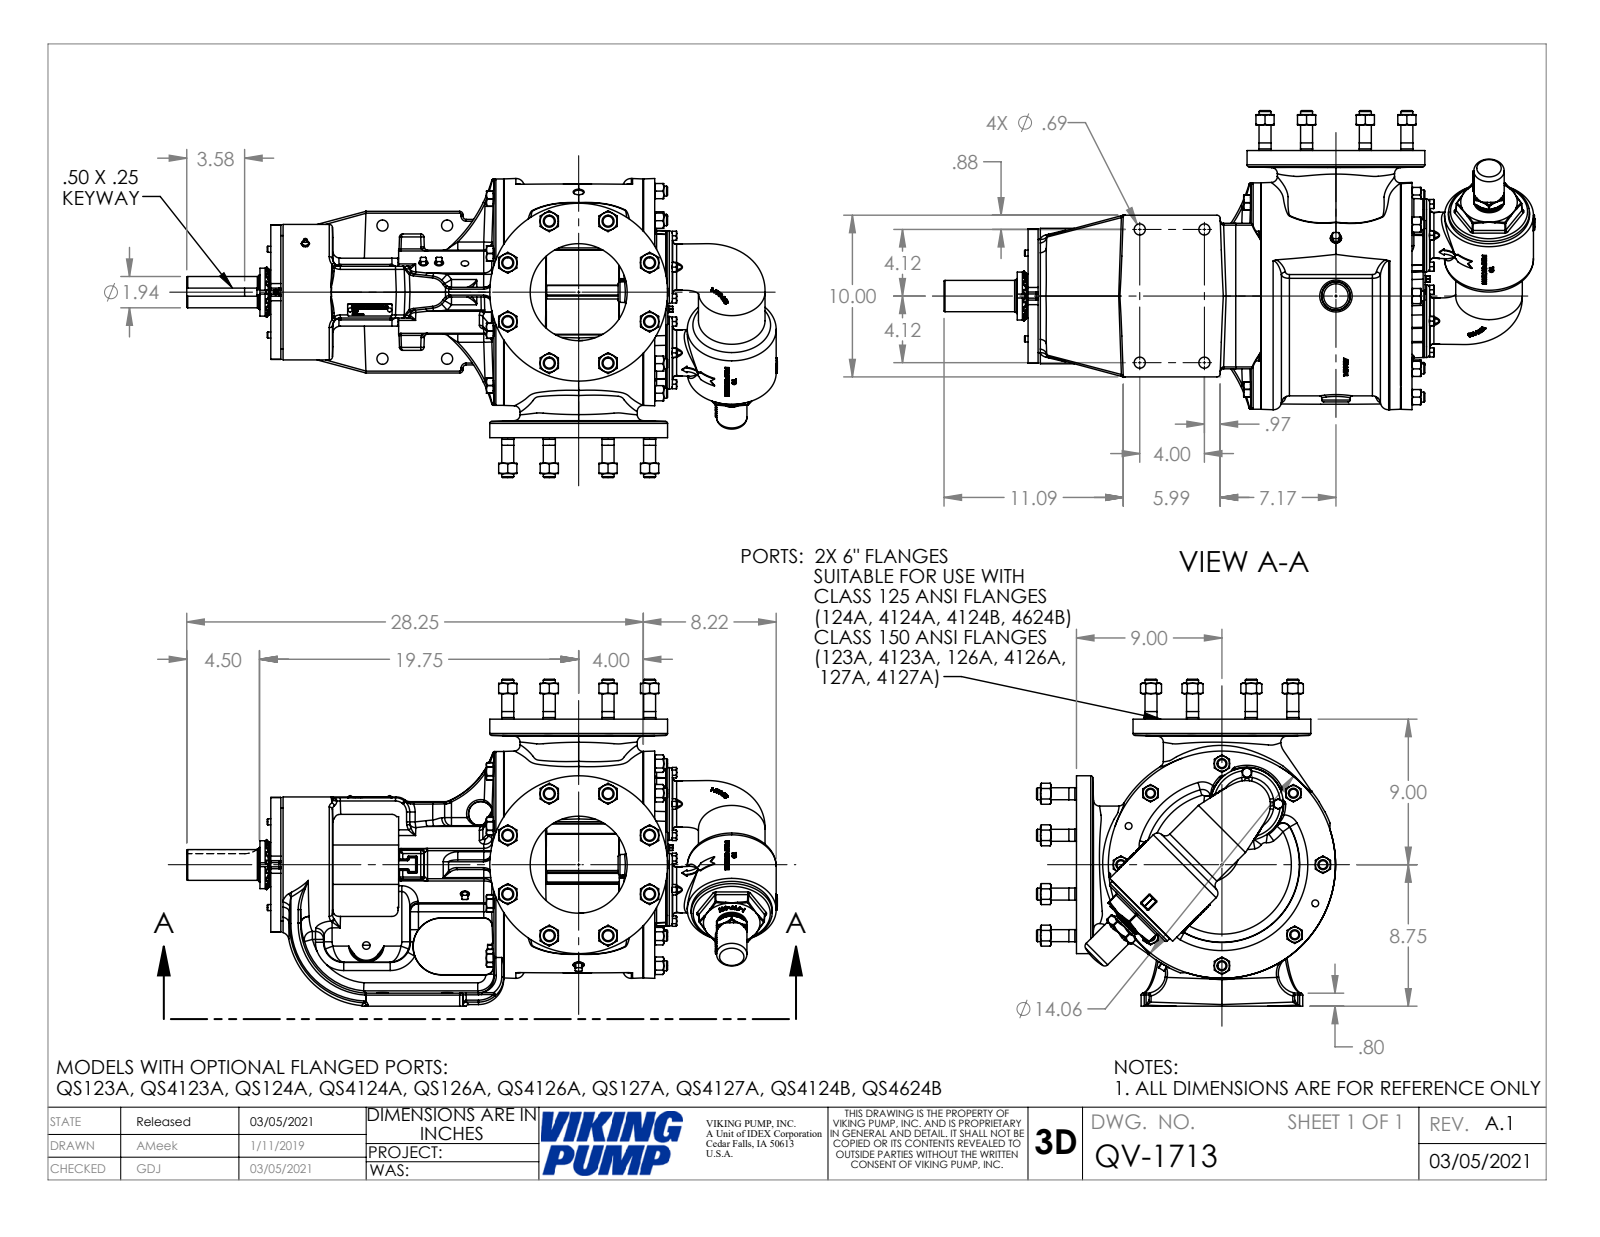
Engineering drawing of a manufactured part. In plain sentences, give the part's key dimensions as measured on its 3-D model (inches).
The part is named "QV-1713". Its 3-D file was written by "SolidWorks 2024 (AUTOMOTIVE_DESIGN)". It is 1 solid with 4638 faces: 1574 planar, 1085 cylindrical and 1979 other. Overall it measures 36.541 by 20.22 by 18.5 inches. Its volume is 2 562 cubic inches and its surface area 2 562 square inches. Round holes: 12 of diameter 0.687, 8 of diameter 0.406, 7 of diameter 0.69, 6 of diameter 0.25, 2 of diameter 0.266, 2 of diameter 0.313, 2 of diameter 0.422, 2 of diameter 6, 1 of diameter 0.468, 1 of diameter 0.594, 1 of diameter 2.157, 1 of diameter 2.167. Round bosses or shafts: 16 of diameter 0.75, 16 of diameter 0.742, 8 of diameter 0.617, 7 of diameter 0.375, 6 of diameter 0.625, 3 of diameter 0.375, 2 of diameter 11, 2 of diameter 4.5. Partial cylindrical surfaces (rounded edges, fillets, slot ends): 104 of radius 0.079, 75 of radius 0.12, 50 of radius 0.5, 42 of radius 0.06, 30 of radius 0.2, 28 of radius 0.079, 18 of radius 0.015, 18 of radius 0.092. The main face-to-face distances are 0.5, 17.75, 20.005, 17.25, 1.5, 4.16, 15.845, 18.505, 14.345, 2.4. The hole center spacings are 3.75, 3.133, 5.932, 6.25, 8.43, 8.839, 9.82, 11.549.
